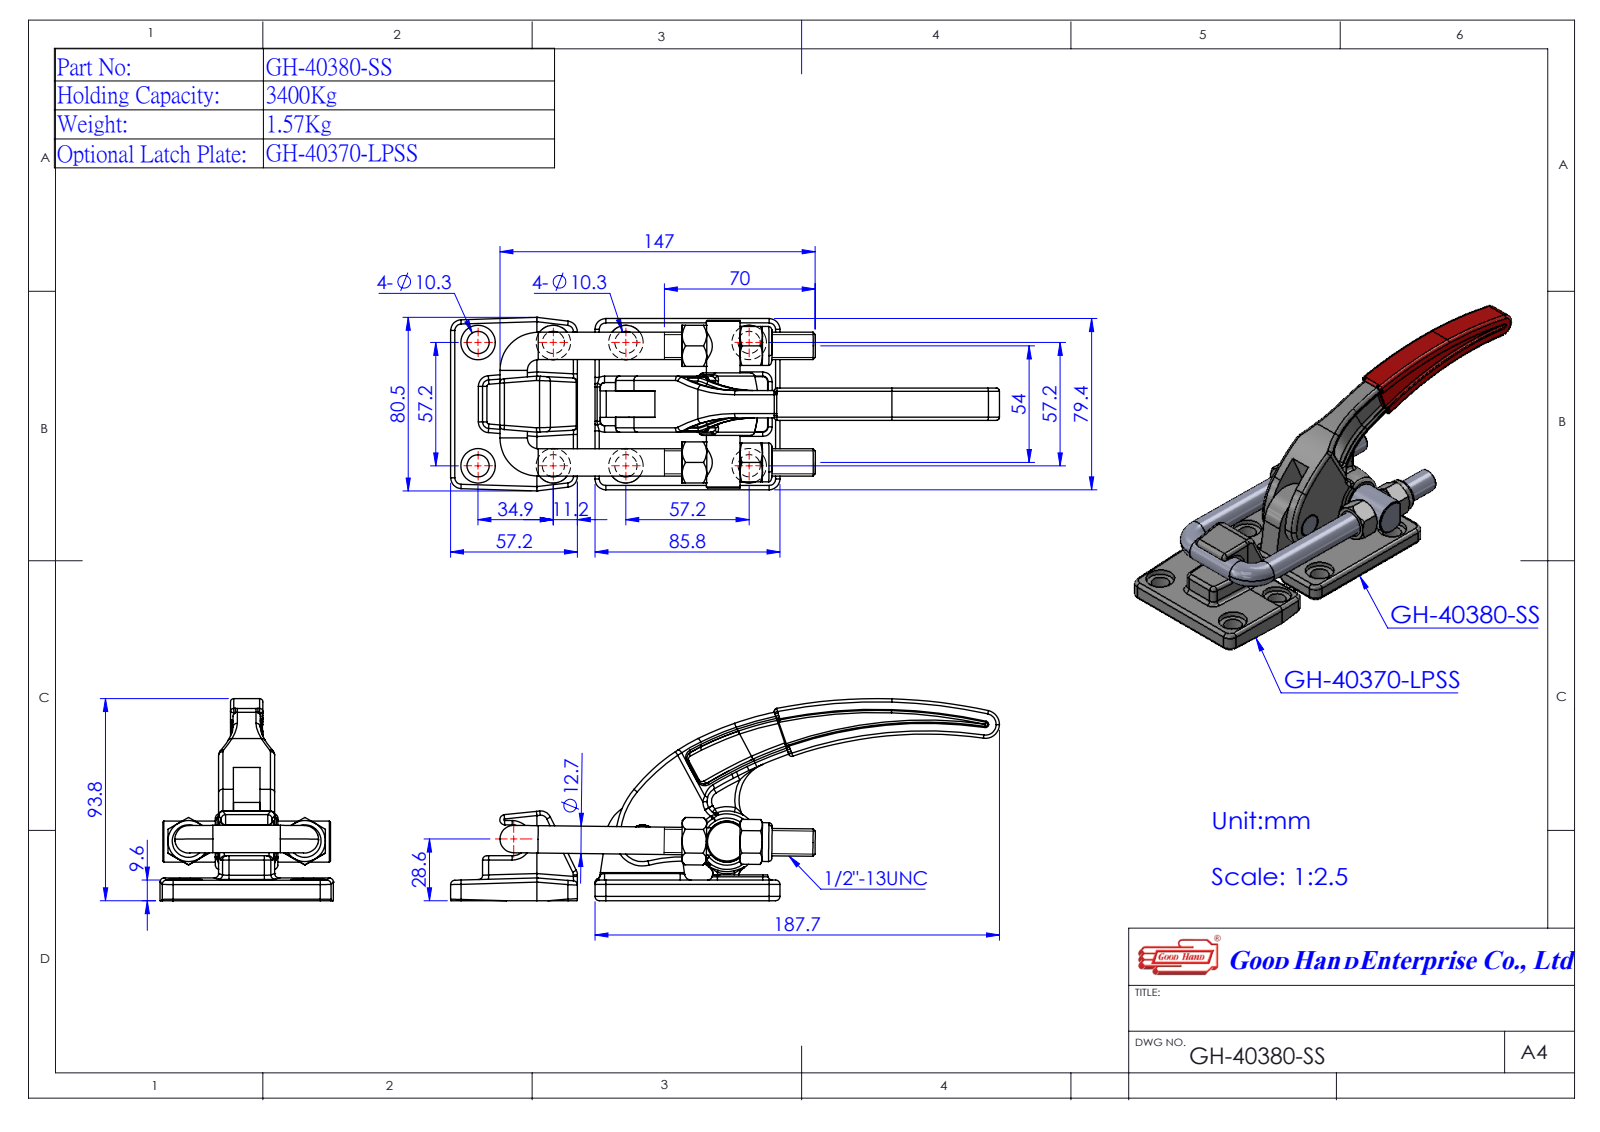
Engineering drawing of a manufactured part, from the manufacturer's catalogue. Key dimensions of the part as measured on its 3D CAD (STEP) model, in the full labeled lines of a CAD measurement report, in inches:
Part name (STEP PRODUCT): 34038013-1^GH-40380(簡化)-1; 44038044-1^GH-40380(簡化)-1; GH-40380-SS(簡化)-1; Group1^GH-40380(簡化)-1 (+1 more)
STEP written by: SolidWorks 2016 (AUTOMOTIVE_DESIGN)
Units: inches
Bodies: 6 solids, 355 faces (105 planar, 124 cylindrical, 126 other)
Overall size (bounding box): 9.943 × 3.691 × 3.126
Volume: 13.26 in³ · Surface area: 106.8 in²
Round holes (diameter × count): ⌀0.406 ×4, ⌀0.63 ×4, ⌀0.402 ×2, ⌀0.422 ×2, ⌀0.472 ×2, ⌀0.5 ×2, ⌀0.504 ×2, ⌀0.54 ×2, ⌀0.394 ×1, ⌀0.748 ×1
Round bosses / shafts (diameter × count): ⌀0.5 ×3, ⌀0.709 ×2
Partial cylindrical surfaces — rounded edges, fillets, slot ends (radius × count): R0.079 ×20, R0.197 ×4, R0.255 ×2, R2.586 ×2, R2.704 ×2, R0.039 ×1, R0.256 ×1, R0.492 ×1
Main face-to-face distances: 0.378, 0.266, 0.758, 0.807, 0.217, 0.049, 0.541, 0.276, 0.492, 0.079
Hole centre spacings: 2.126, 2.252, 3.185, 1.545
